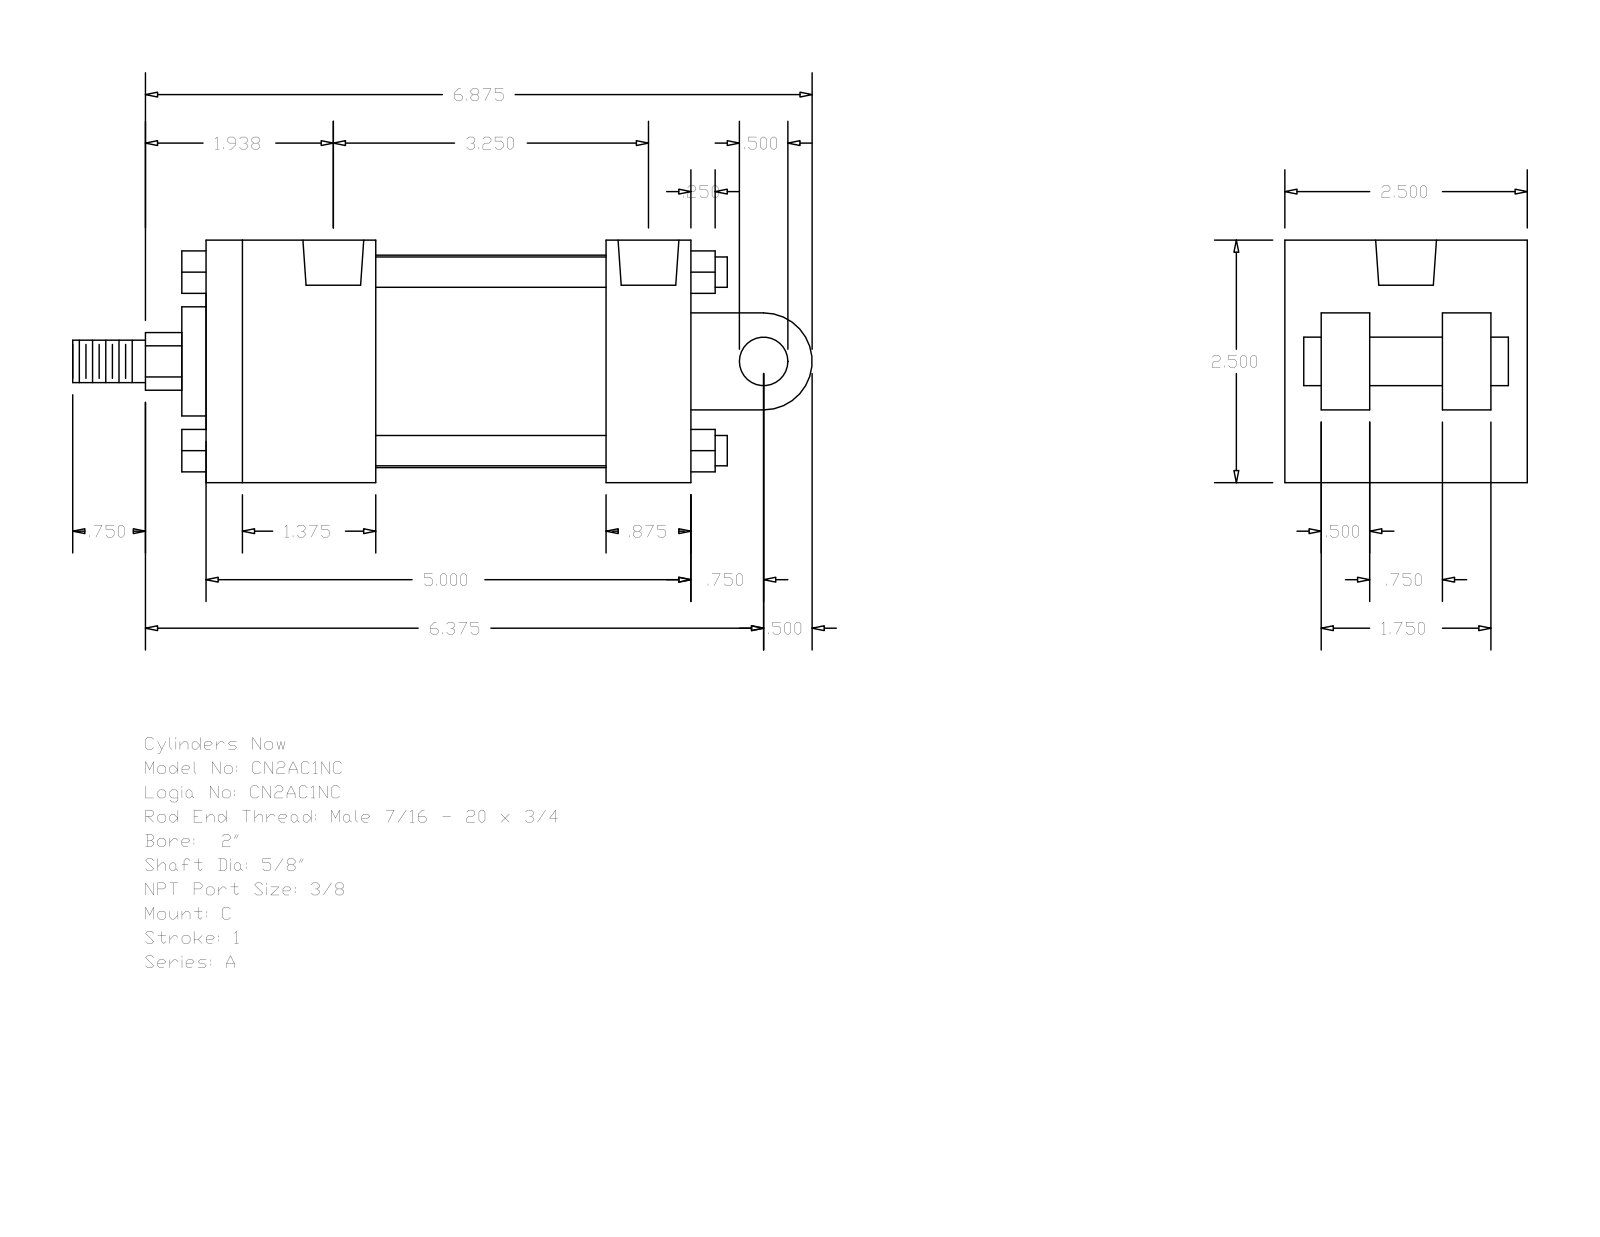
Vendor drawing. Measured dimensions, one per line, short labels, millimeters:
name: A_C__0200_0.625
written by: GSSL Pune (CONFIG_CONTROL_DESIGN)
unit: mm
bodies: 0 solids, 135 faces (102 planar, 33 cylindrical, 0 other)
size: 193.68 × 63.5 × 63.5
holes: 4× ⌀5.56, 2× ⌀15.93
bosses: 4× ⌀7.94, 1× ⌀55.63, 1× ⌀28.57, 1× ⌀15.88, 1× ⌀12.7, 1× ⌀11.11
rounds: 1× R7.54, 1× R12.7
face distances: 63.5, 127, 44.45, 9.52, 82.55, 104.77, 60.32, 22.23, 12.7, 53.98
hole spacings: 74.6, 3.97, 3.98, 78.57, 78.58, 82.55
